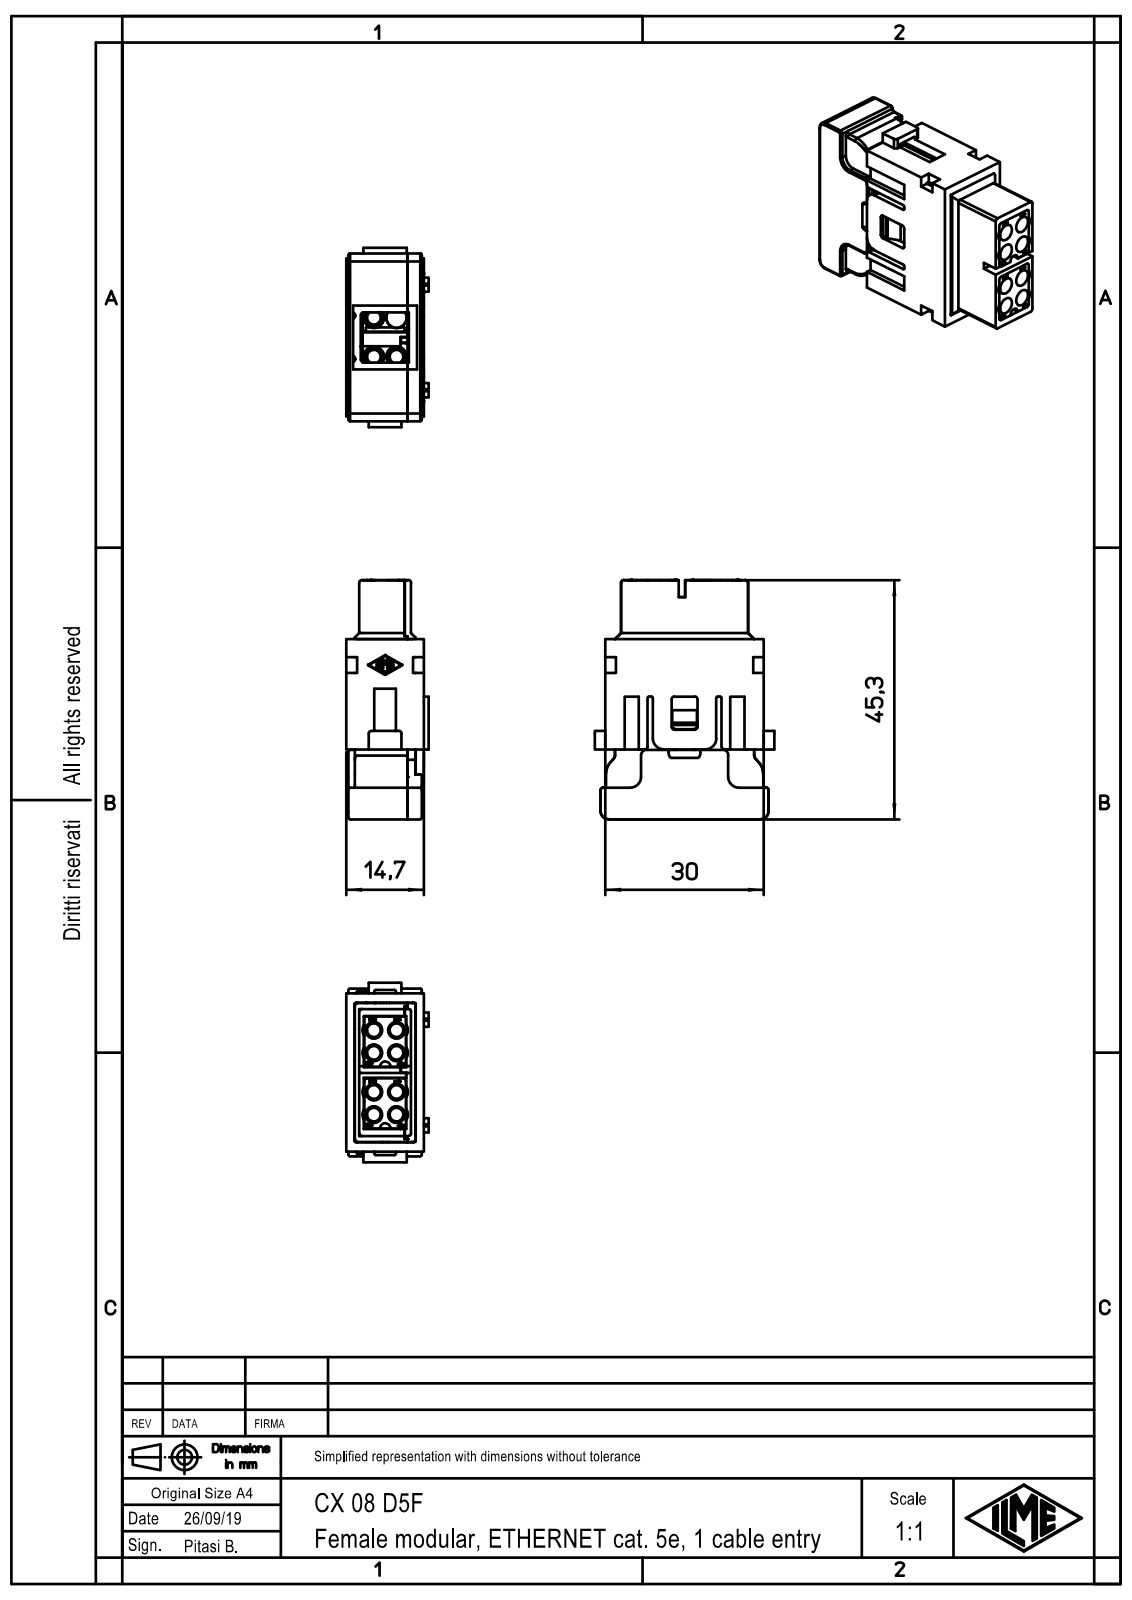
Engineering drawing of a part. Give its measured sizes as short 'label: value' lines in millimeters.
name: CX 08 D5F
written by: Creo Elements/Direct Modeling 20.1B 02-Apr-2019 (C) Parametric Technology GmbH (AUTOMOTIVE_DESIGN)
unit: mm
bodies: 1 solid, 623 faces (375 planar, 167 cylindrical, 81 other)
size: 45.3 × 34 × 15.6
volume: 15 182 mm³; area: 10 588 mm²
holes: 2× ⌀2.6, 2× ⌀5
bosses: 2× ⌀4.7, 2× ⌀1.9
rounds: 53× R0.5, 36× R0.3, 8× R1, 6× R2, 4× R0.2, 4× R0.4, 4× R2.15, 2× R1.5
face distances: 0.9, 10.65, 1.6, 13.1, 13.15, 1.55, 11.55, 1.15, 1.2, 12.1
hole spacings: 22.6
